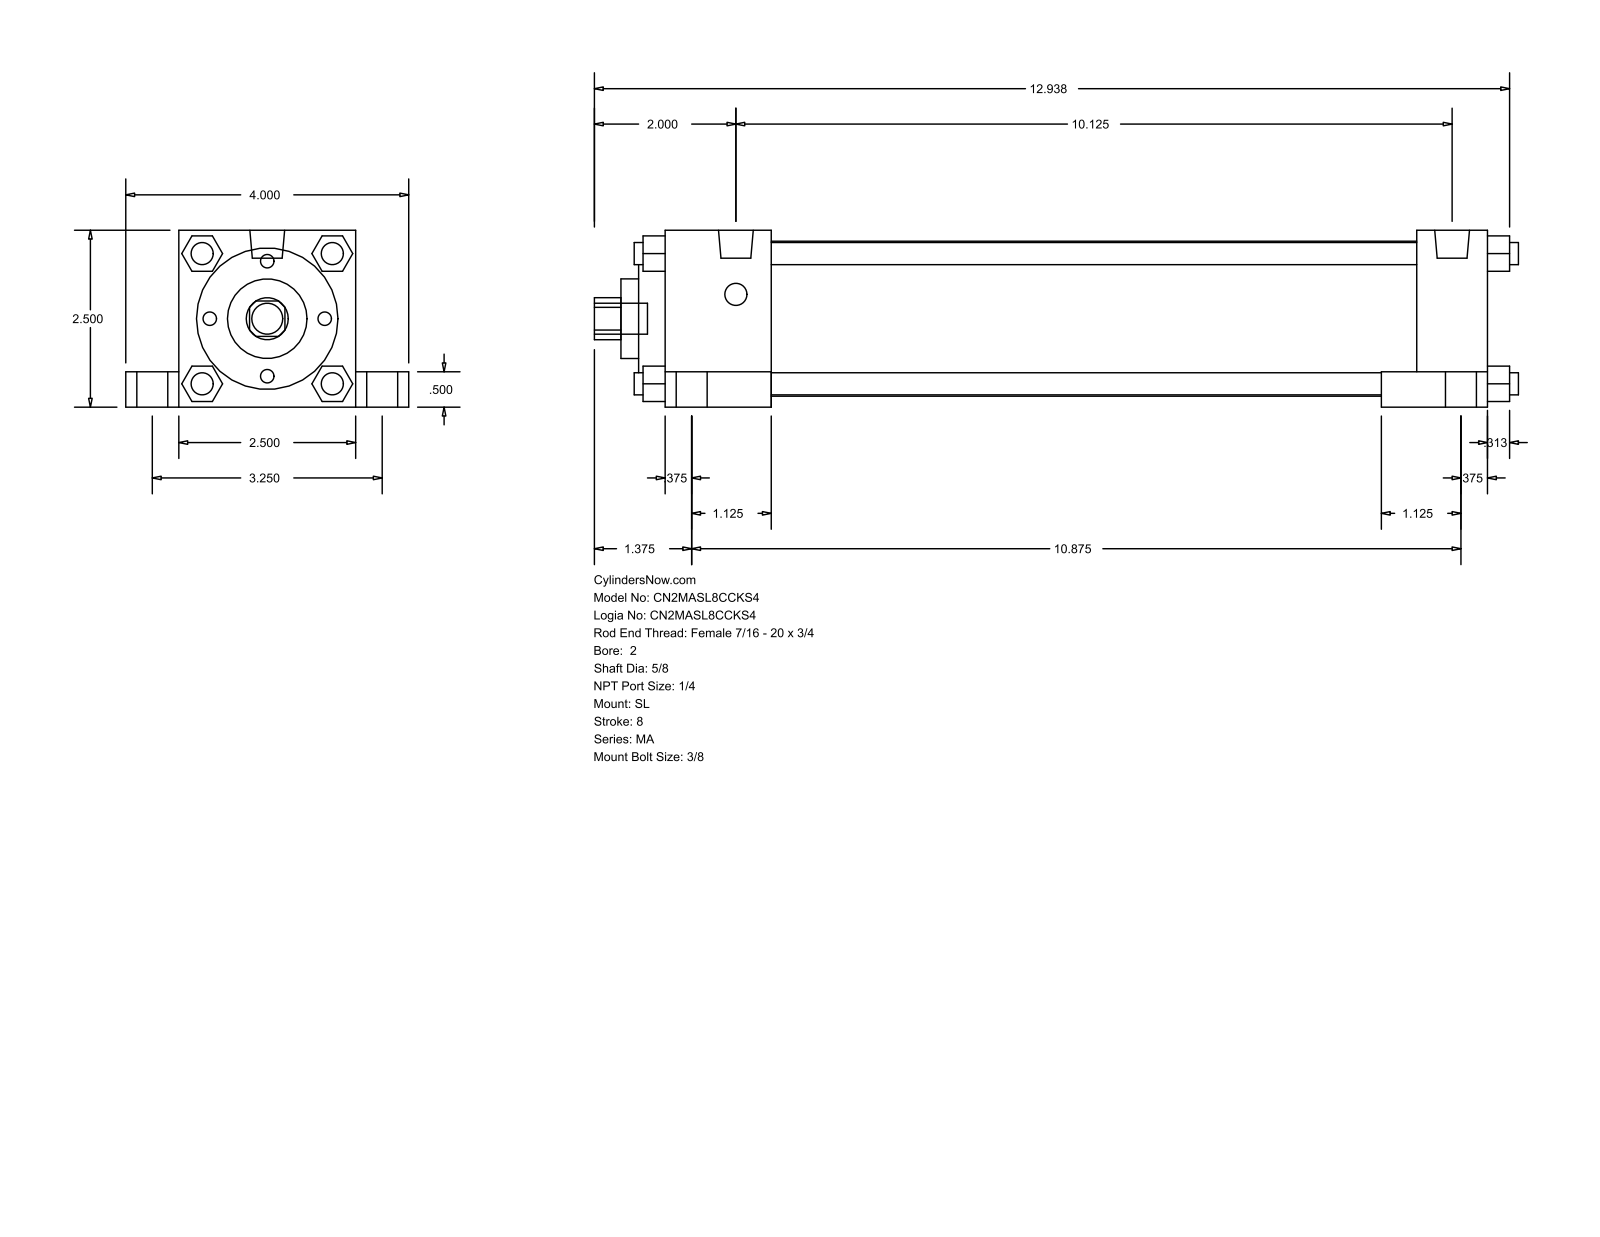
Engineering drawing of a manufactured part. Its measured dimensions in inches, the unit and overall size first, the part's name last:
Units: inches
Overall size (bounding box): 13.063 × 4 × 2.5
Round holes (diameter × count): ⌀0.625 ×1, ⌀1.125 ×1, ⌀2 ×1, ⌀2.19 ×1
Round bosses / shafts (diameter × count): ⌀0.313 ×8, ⌀0.437 ×5, ⌀0.687 ×4, ⌀0.492 ×2
Partial cylindrical surfaces — rounded edges, fillets, slot ends (radius × count): R0.297 ×1
Main face-to-face distances: 2.5, 0.5, 0.375, 9.125, 0.75, 3.25, 1.5, 2, 11.625, 10.125
Bodies: 0 solids, 150 faces (113 planar, 37 cylindrical, 0 other)
Part name (STEP PRODUCT): MA_SL__0200_0.625
STEP written by: GSSL Pune (CONFIG_CONTROL_DESIGN)
